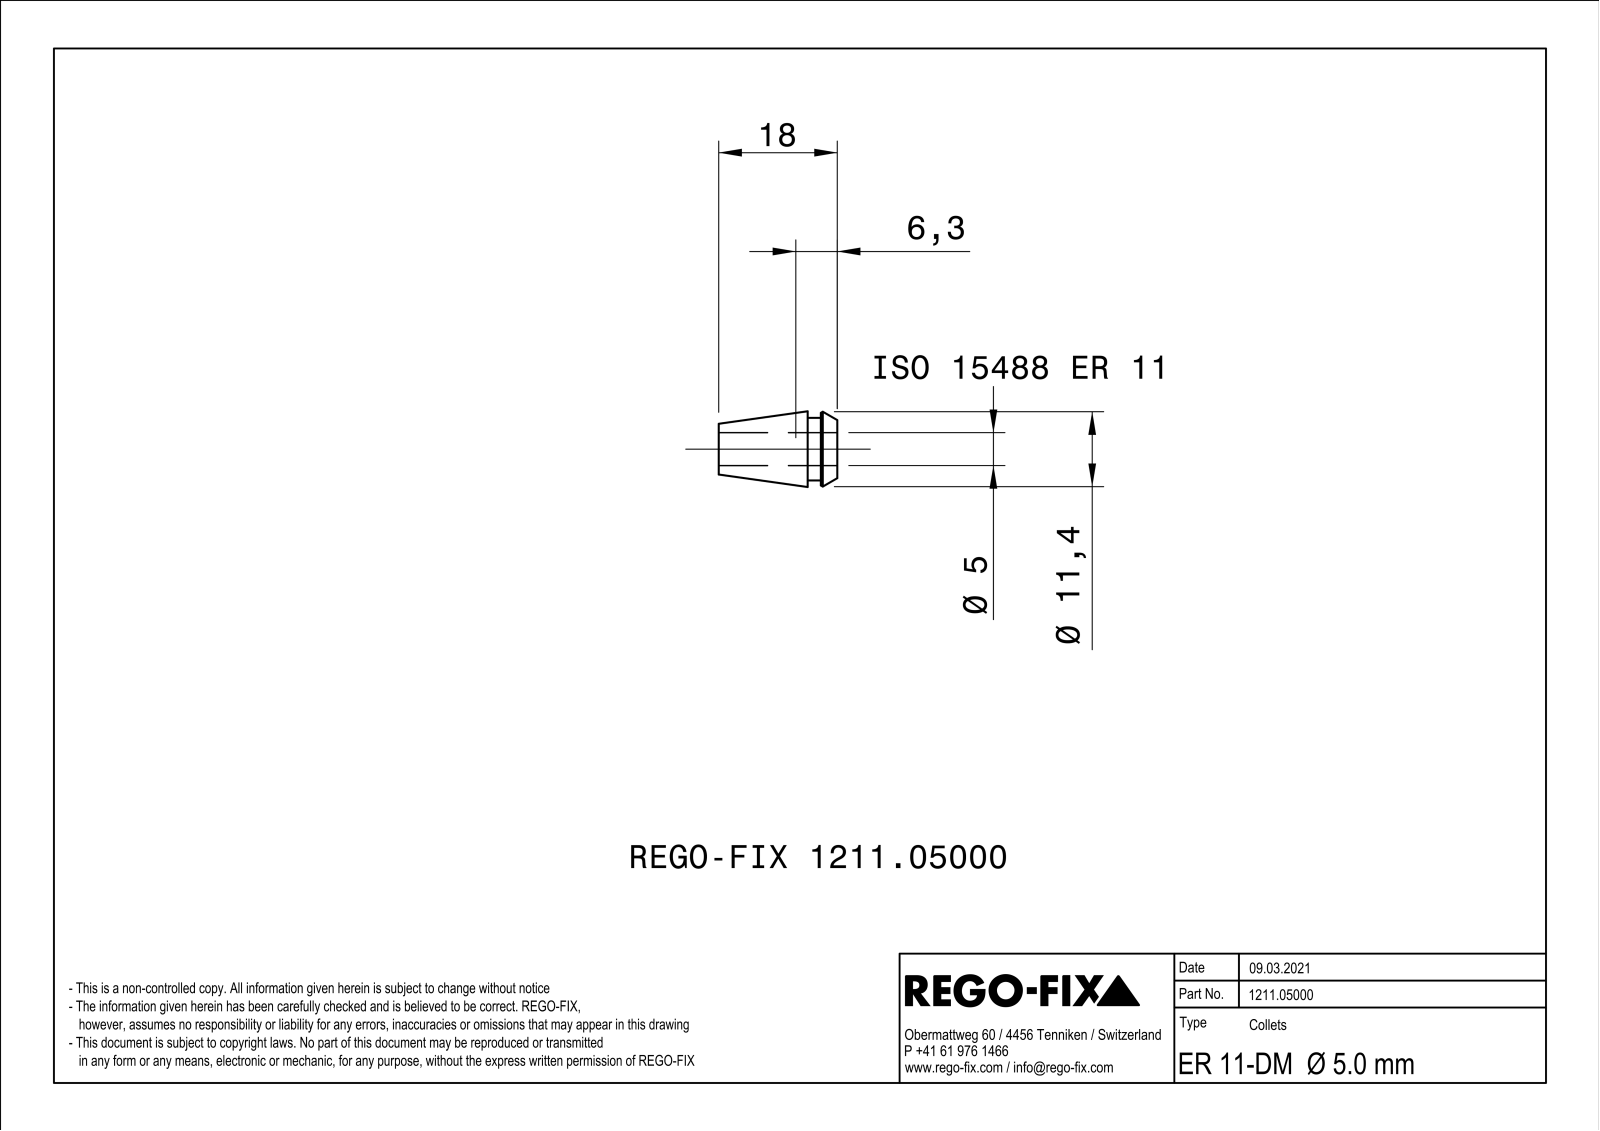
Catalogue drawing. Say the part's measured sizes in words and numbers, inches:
The part is named "NOCUT". Its 3-D file was written by "SIEMENS PLM Software Solid Edge ST10 (AUTOMOTIVE_DESIGN)". It is 1 solid with 116 faces: 48 planar, 19 cylindrical and 49 other. Overall it measures 0.709 by 0.453 by 0.452 inches. Its volume is 0.05 cubic inches and its surface area 2.306 square inches. Round holes: 1 of diameter 0.197. Round bosses or shafts: 1 of diameter 0.374. Partial cylindrical surfaces (rounded edges, fillets, slot ends): 6 of radius 0.01. The main face-to-face distances are 0.02, 0.177, 0.098, 0.079, 0.709, 0.61, 0.531.
